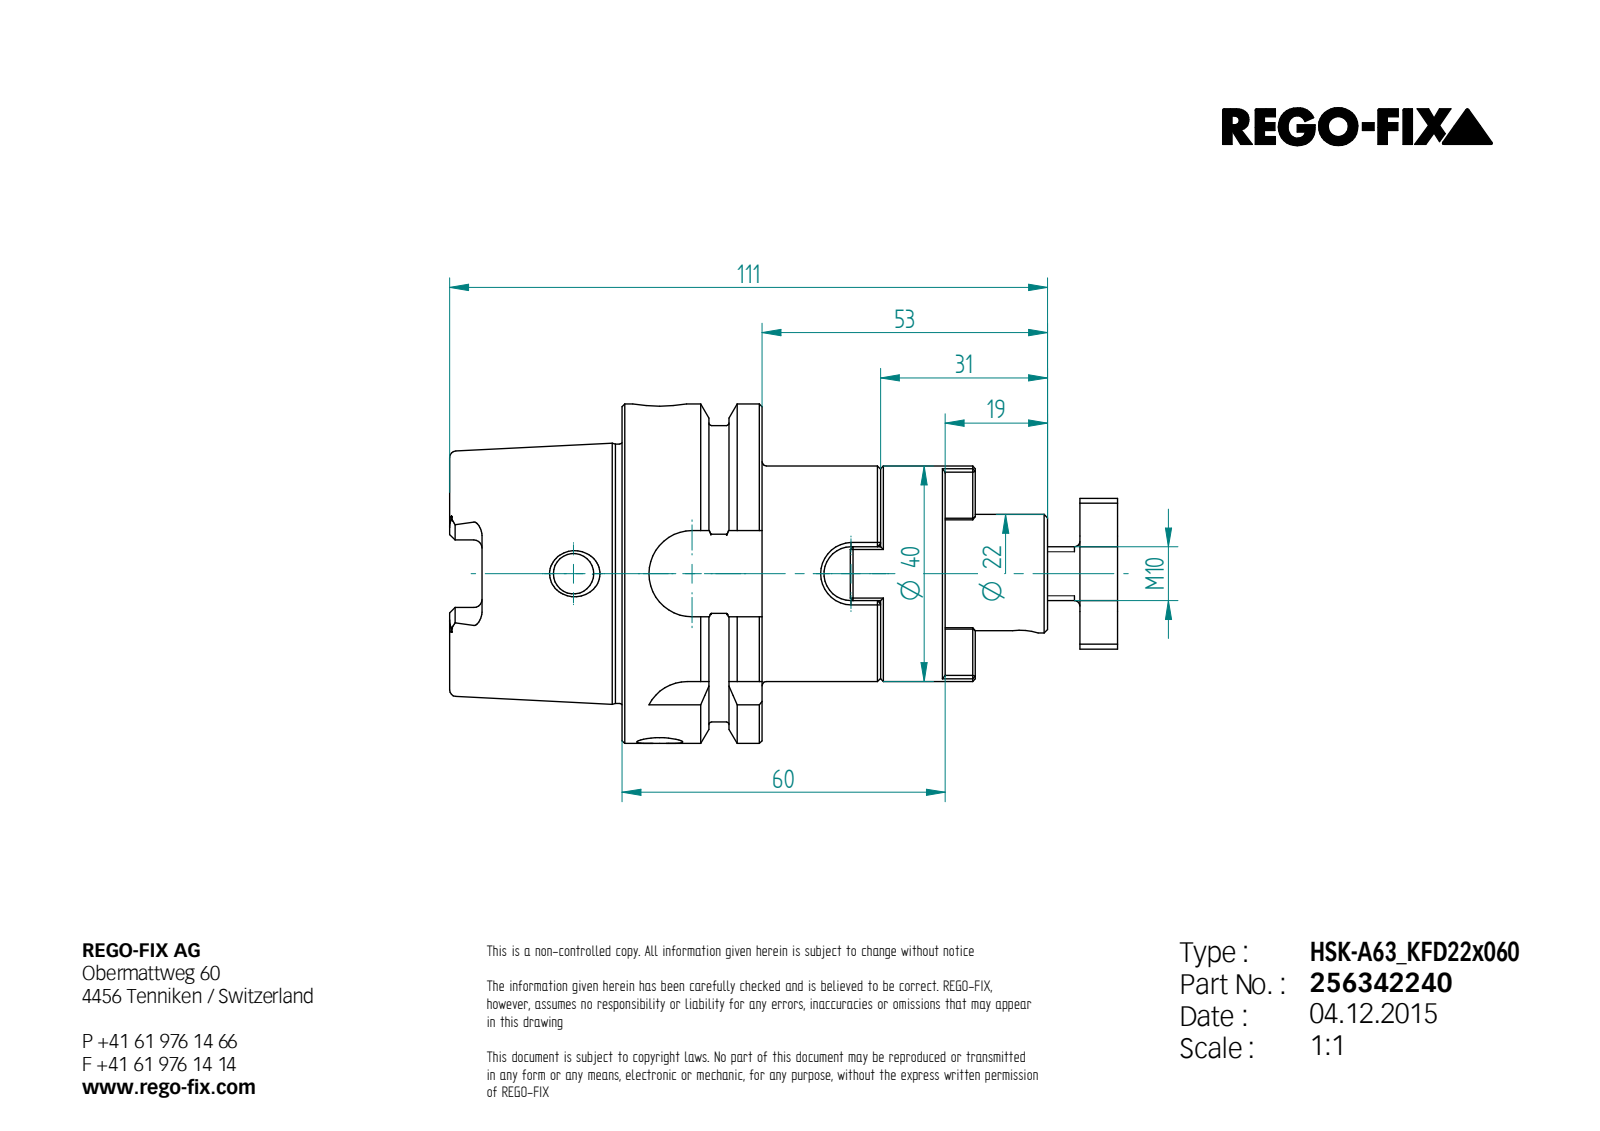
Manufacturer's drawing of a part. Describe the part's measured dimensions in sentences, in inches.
Its 3-D file was written by "Unknown (AUTOMOTIVE_DESIGN)". It is 3 solids with 260 faces: 134 planar, 51 cylindrical and 75 other. Overall it measures 4.882 by 2.48 by 2.48 inches. Its volume is 8.068 cubic inches and its surface area 55.75 square inches. Round holes: 1 of diameter 0.295, 1 of diameter 0.33, 1 of diameter 0.335, 1 of diameter 0.394, 1 of diameter 0.413, 1 of diameter 0.666, 1 of diameter 0.787, 1 of diameter 0.866, 1 of diameter 1.339. Round bosses or shafts: 1 of diameter 2.48, 1 of diameter 2.165, 1 of diameter 1.895, 1 of diameter 1.575, 1 of diameter 0.843, 1 of diameter 0.394. Partial cylindrical surfaces (rounded edges, fillets, slot ends): 6 of radius 0.059, 4 of radius 0.079, 4 of radius 0.113, 4 of radius 0.315, 2 of radius 0.118, 1 of radius 0.197, 1 of radius 0.551. The main face-to-face distances are 0.866, 1.024, 1.89, 0.394, 1.496, 0.472, 1.26, 3.622, 2.362, 1.339.
